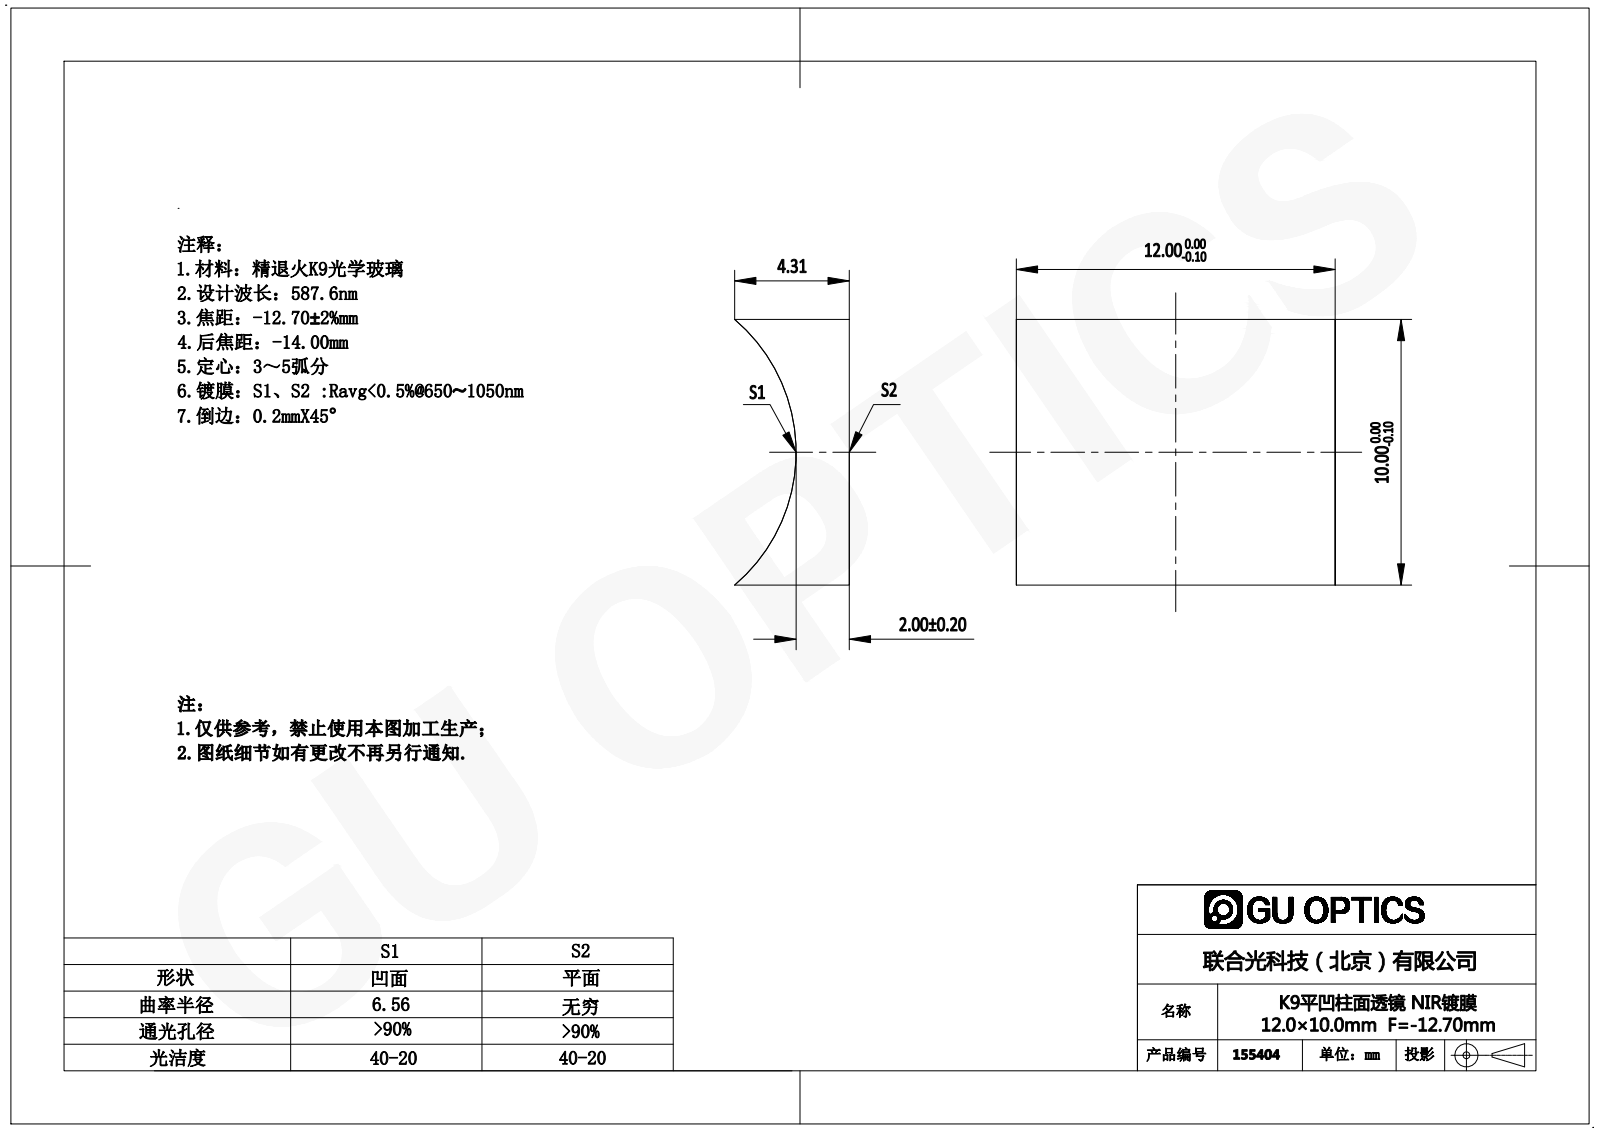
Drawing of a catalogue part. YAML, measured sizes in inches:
part_name: "155338"
step_written_by: "SolidWorks 2016 (AUTOMOTIVE_DESIGN)"
units: inches
bodies: {solids: 1, faces: 6, planar: 5, cylindrical: 1, other: 0}
overall_size: [0.472, 0.394, 0.17]
volume: 0.02
surface_area: 0.642
partial_cylinders:
  - {radius: 0.258, count: 1}
face_to_face_distances: [0.394, 0.472]
